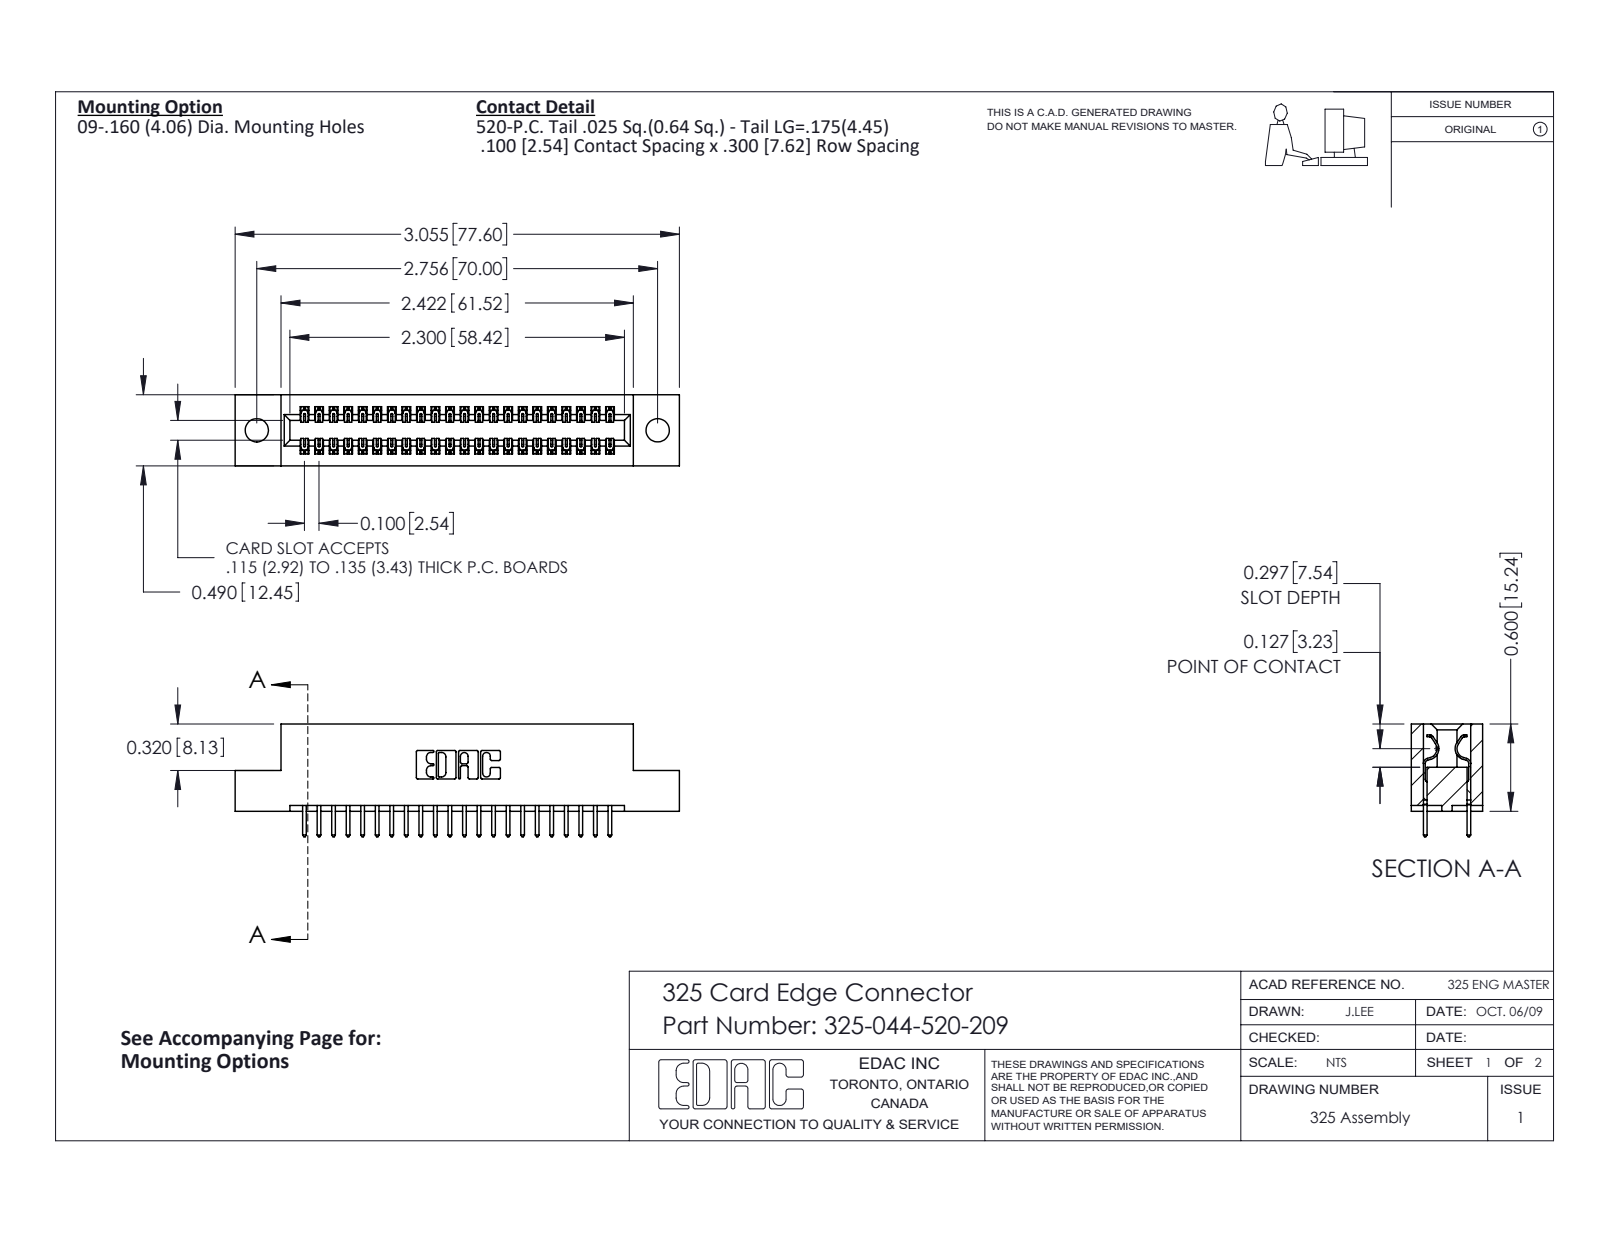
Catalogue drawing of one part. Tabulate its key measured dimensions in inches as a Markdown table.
| quantity | value |
| --- | --- |
| part name | 325-292-001_325-293-120; 325 Part_.160 TH; 325-044-520-209 |
| STEP written by | SolidWorks 2016 (CONFIG_CONTROL_DESIGN) |
| units | inches |
| bodies | 45 solids, 2402 faces (1654 planar, 748 cylindrical, 0 other) |
| overall size | 3.055 × 0.775 × 0.49 |
| volume | 0.586 in³ |
| surface area | 17.02 in² |
| round holes (diameter × count) | 0.16 × 2 |
| partial cylindrical surfaces (radius × count) | 0.006 × 66, 0.01 × 44, 0.01 × 22, 0.007 × 6, 0.031 × 6, 0.026 × 3, 0.014 × 2, 0.022 × 2 |
| main face-to-face distances | 0.083, 0.407, 0.3, 0.49, 0.107, 0.383, 0.025, 0.325, 0.04, 0.1 |
| hole center spacings | 2.756 |
